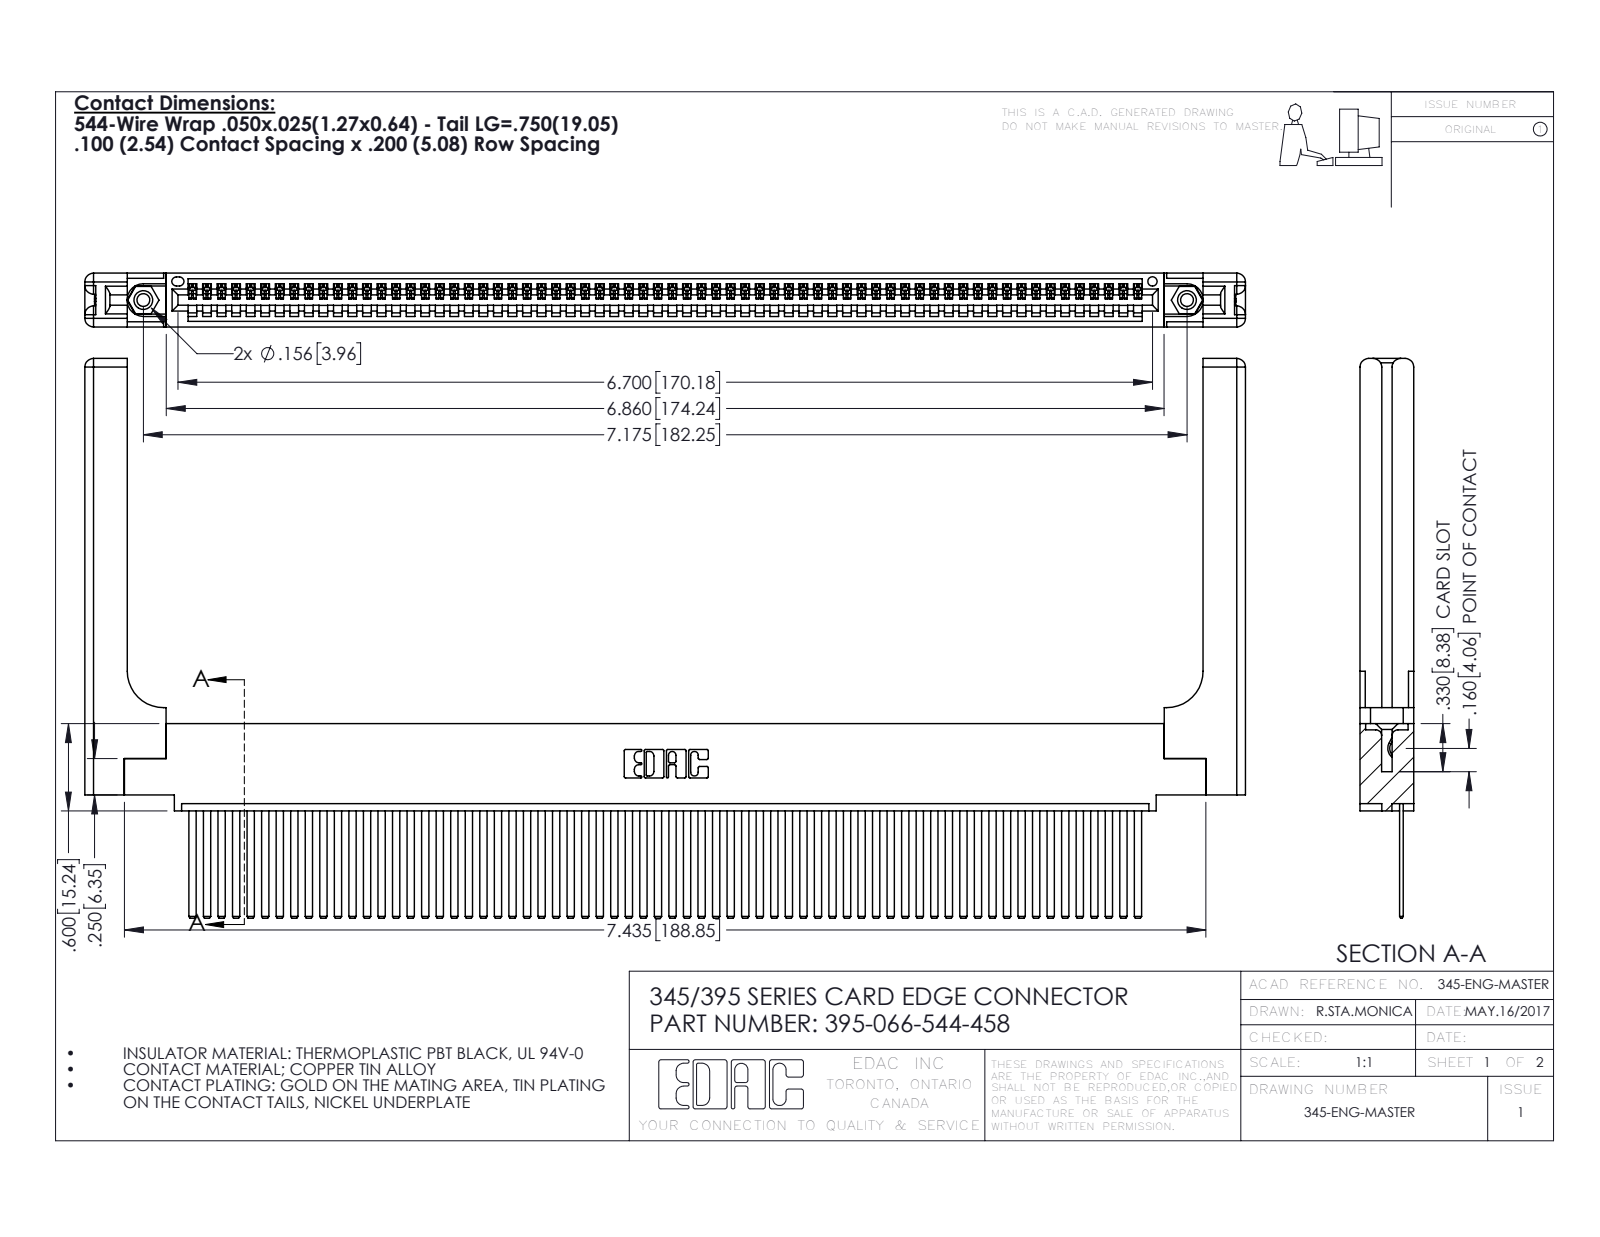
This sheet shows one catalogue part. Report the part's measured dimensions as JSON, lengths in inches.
{"part_name": "345-220-058_345-220-058; 345-292-001_345-293-144; 345-250-001_345-250-001-102; 395-066-544-458 (+1 more)", "step_written_by": "SolidWorks 2016 (CONFIG_CONTROL_DESIGN)", "units": "inches", "bodies": {"solids": 71, "faces": 3818, "planar": 2608, "cylindrical": 1150, "other": 60}, "overall_size": [7.979, 3.847, 0.37], "volume_in3": 1.748, "surface_area_in2": 53.89, "round_holes": [[0.089, 2], [0.125, 2], [0.156, 2], [0.064, 1]], "round_bosses_or_shafts": [[0.155, 2]], "partial_cylinders_radius": [[0.006, 132], [0.01, 22], [0.06, 16], [0.007, 6], [0.031, 6], [0.026, 3], [0.03, 2], [0.031, 2]], "face_to_face_distances": [0.072, 0.298, 0.098, 0.272, 0.025, 0.37, 0.2, 0.225, 0.148, 0.15], "hole_center_spacings": [0.27, 6.939, 7.175]}
